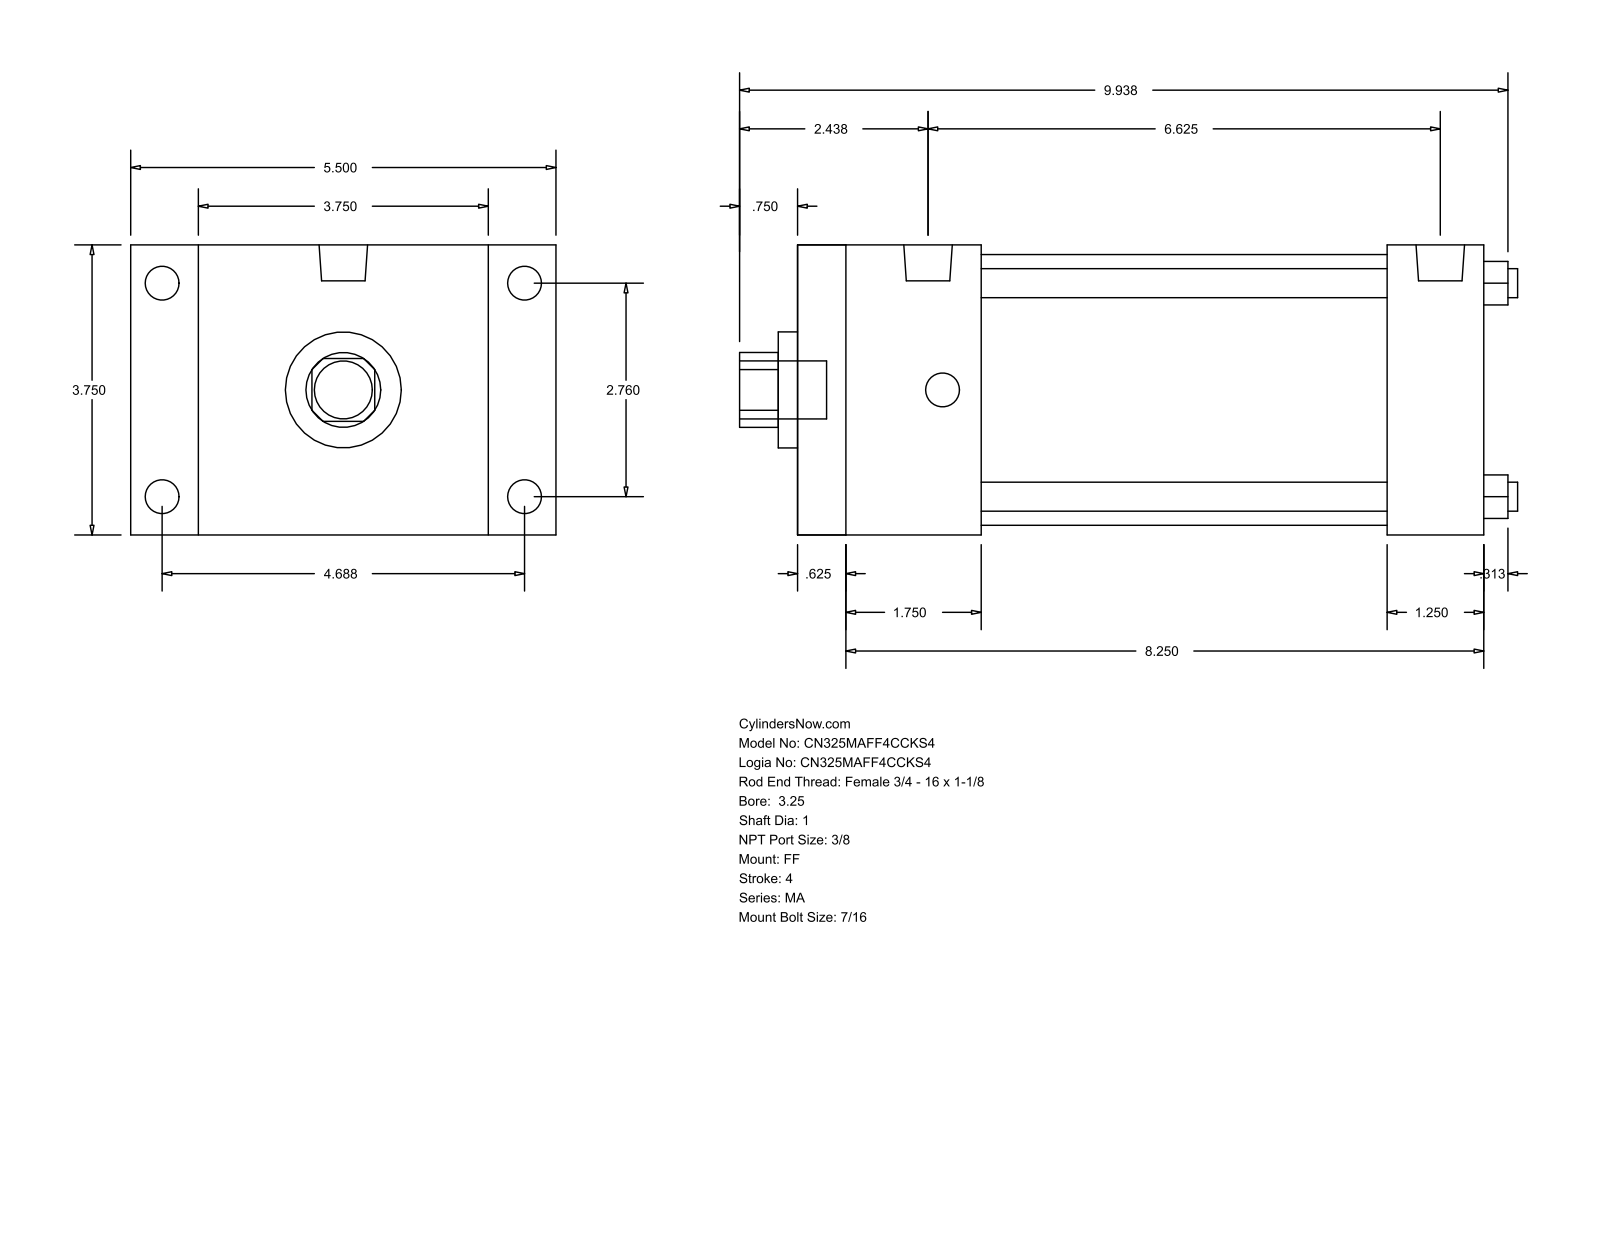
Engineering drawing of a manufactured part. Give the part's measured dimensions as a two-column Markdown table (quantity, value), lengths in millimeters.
| quantity | value |
| --- | --- |
| part name | MA_FF__0325_1 |
| STEP written by | GSSL Pune (CONFIG_CONTROL_DESIGN) |
| units | millimeters |
| bodies | 0 solids, 92 faces (64 planar, 28 cylindrical, 0 other) |
| overall size | 255.59 × 139.7 × 95.25 |
| round holes (diameter × count) | 9.53 × 4, 25.4 × 1, 38.1 × 1, 88.9 × 1 |
| round bosses / shafts (diameter × count) | 11.11 × 8, 15.93 × 2, 19.05 × 1 |
| partial cylindrical surfaces (radius × count) | 12.29 × 1 |
| main face-to-face distances | 95.24, 225.42, 15.87, 209.55, 22.23, 117.47, 60.33, 193.67, 44.46, 177.8 |
| hole center spacings | 49.57, 70.1, 99.14 |
